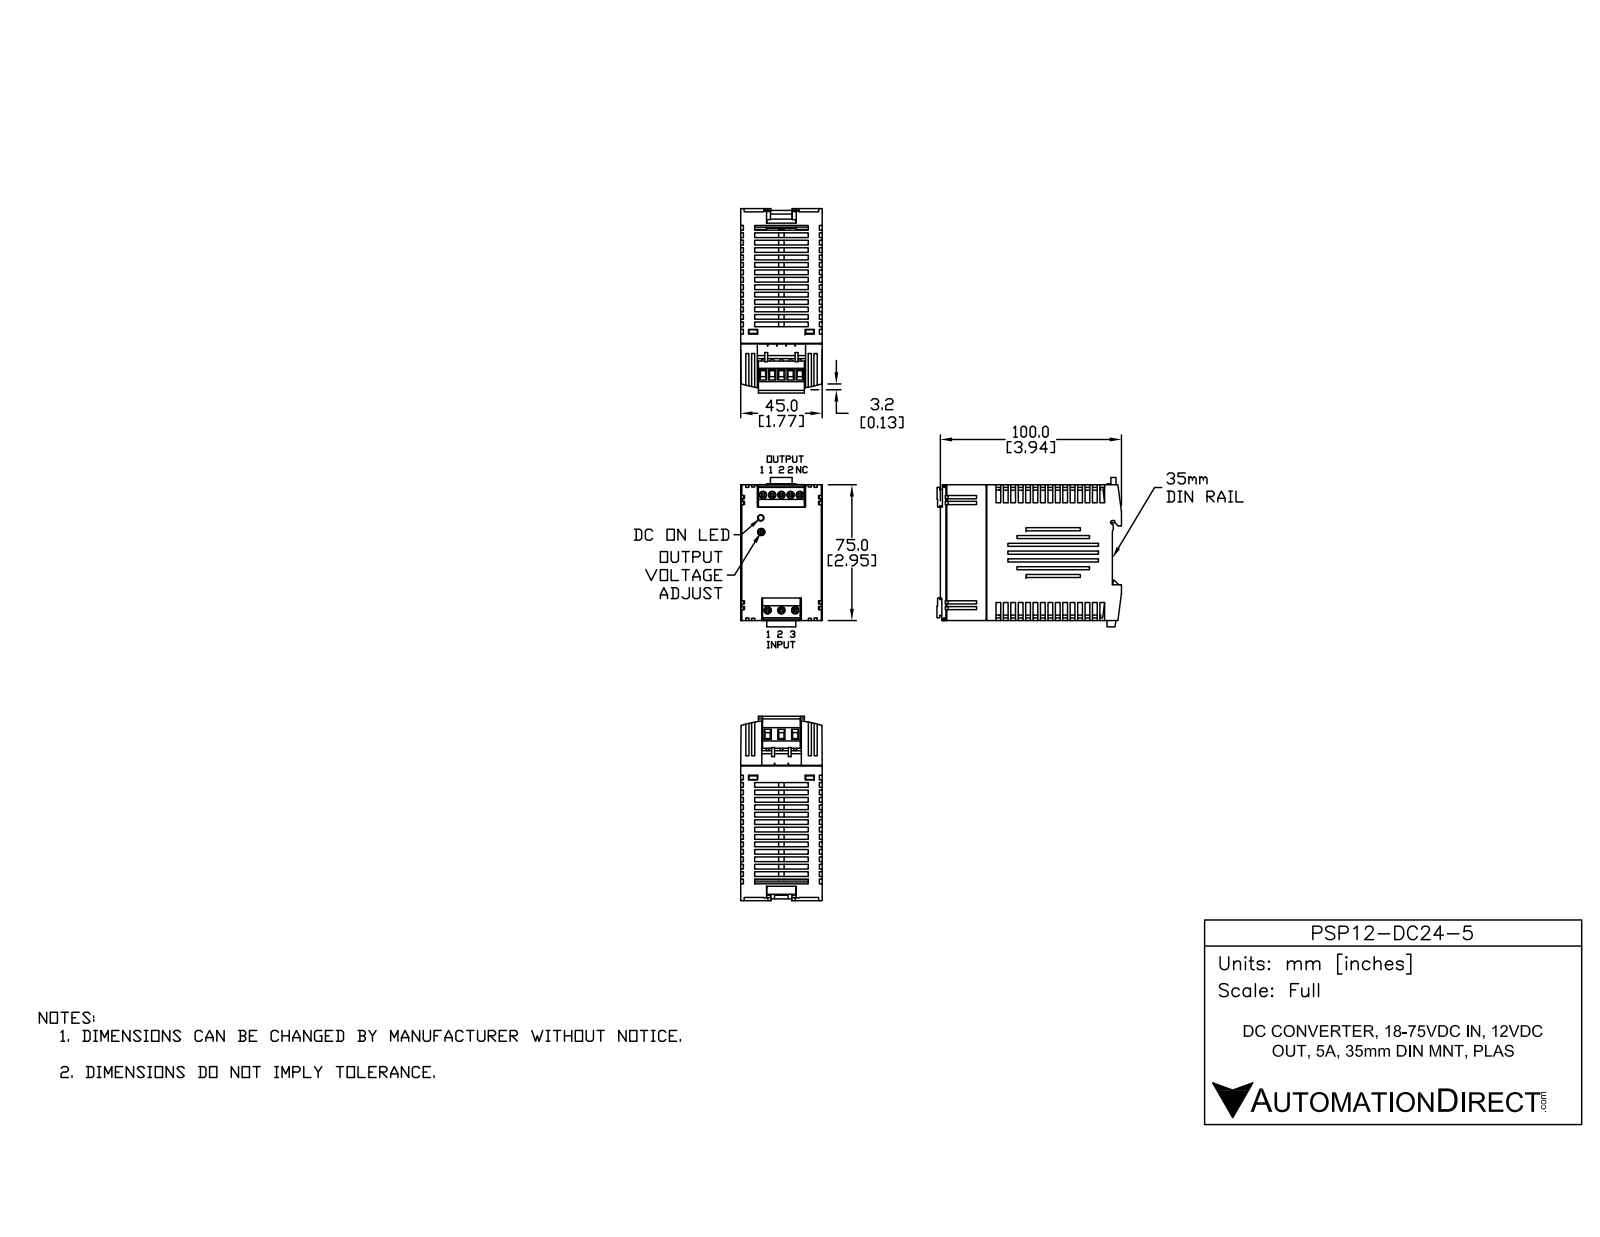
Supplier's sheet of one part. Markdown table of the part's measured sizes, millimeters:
| quantity | value |
| --- | --- |
| part name | PSP12-DC24-5 |
| STEP written by | SolidWorks 2015 (AUTOMOTIVE_DESIGN) |
| units | millimeters |
| bodies | 0 solids, 1218 faces (1068 planar, 145 cylindrical, 5 other) |
| overall size | 101.86 × 82.49 × 45.03 |
| round holes (diameter × count) | 4 × 8, 3.44 × 1, 3.86 × 1, 3.91 × 1 |
| round bosses / shafts (diameter × count) | 1.4 × 2, 0.51 × 1 |
| partial cylindrical surfaces (radius × count) | 0.25 × 30, 0.2 × 5, 1 × 2, 0.3 × 1, 0.75 × 1, 1.5 × 1, 3.5 × 1, 5.5 × 1 |
| main face-to-face distances | 1.5, 43.49, 44.99, 73.5, 41.99, 72, 3, 75, 3.5, 6.5 |
| hole center spacings | 5.08, 63.73, 10.16, 15.24, 7.62, 7.84, 63.88, 64.13 |
